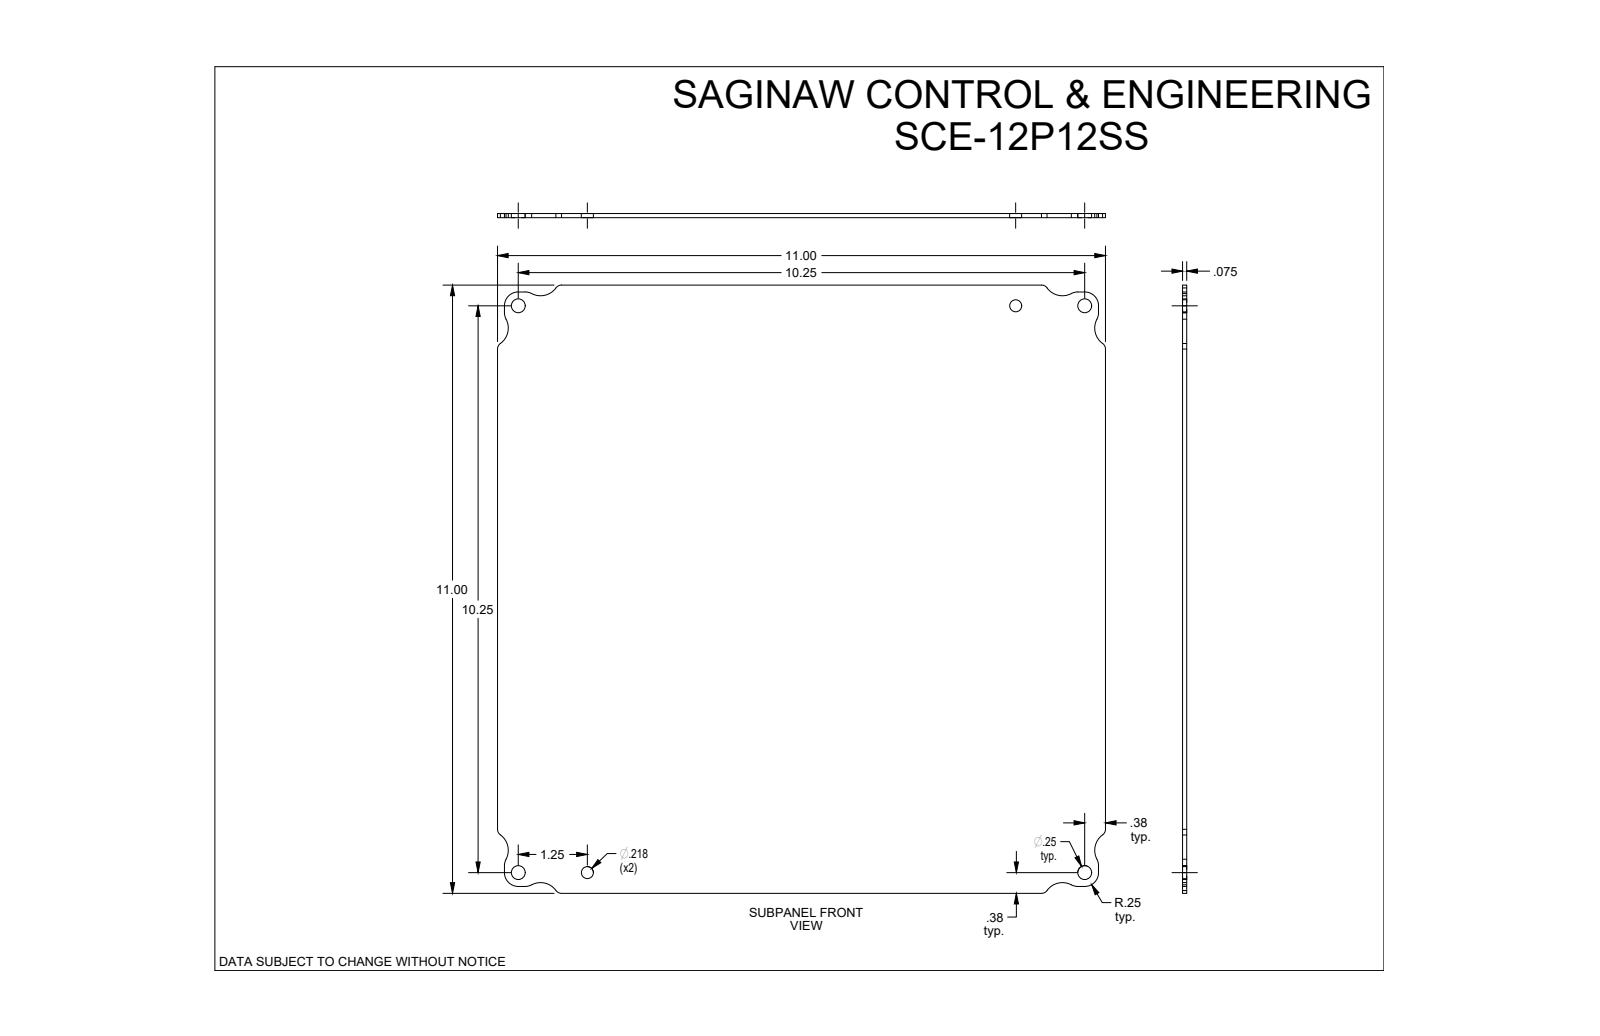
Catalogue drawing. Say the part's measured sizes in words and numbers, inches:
The part is named "SCE-12P12SS". Its 3-D file was written by "SolidWorks 2019 (CONFIG_CONTROL_DESIGN)". It is 1 solid with 48 faces: 14 planar, 34 cylindrical and 0 other. Overall it measures 11 by 11 by 0.075 inches. Its volume is 8.965 cubic inches and its surface area 242.6 square inches. Round holes: 4 of diameter 0.25, 2 of diameter 0.218. Partial cylindrical surfaces (rounded edges, fillets, slot ends): 12 of radius 0.25, 8 of radius 0.125, 8 of radius 0.344. The main face-to-face distances are 0.075, 11, 0.125, 10.875, 10.75. The hole center spacings are 10.25, 1.25, 9, 10.326, 13.64, 14.495, 12.85.
